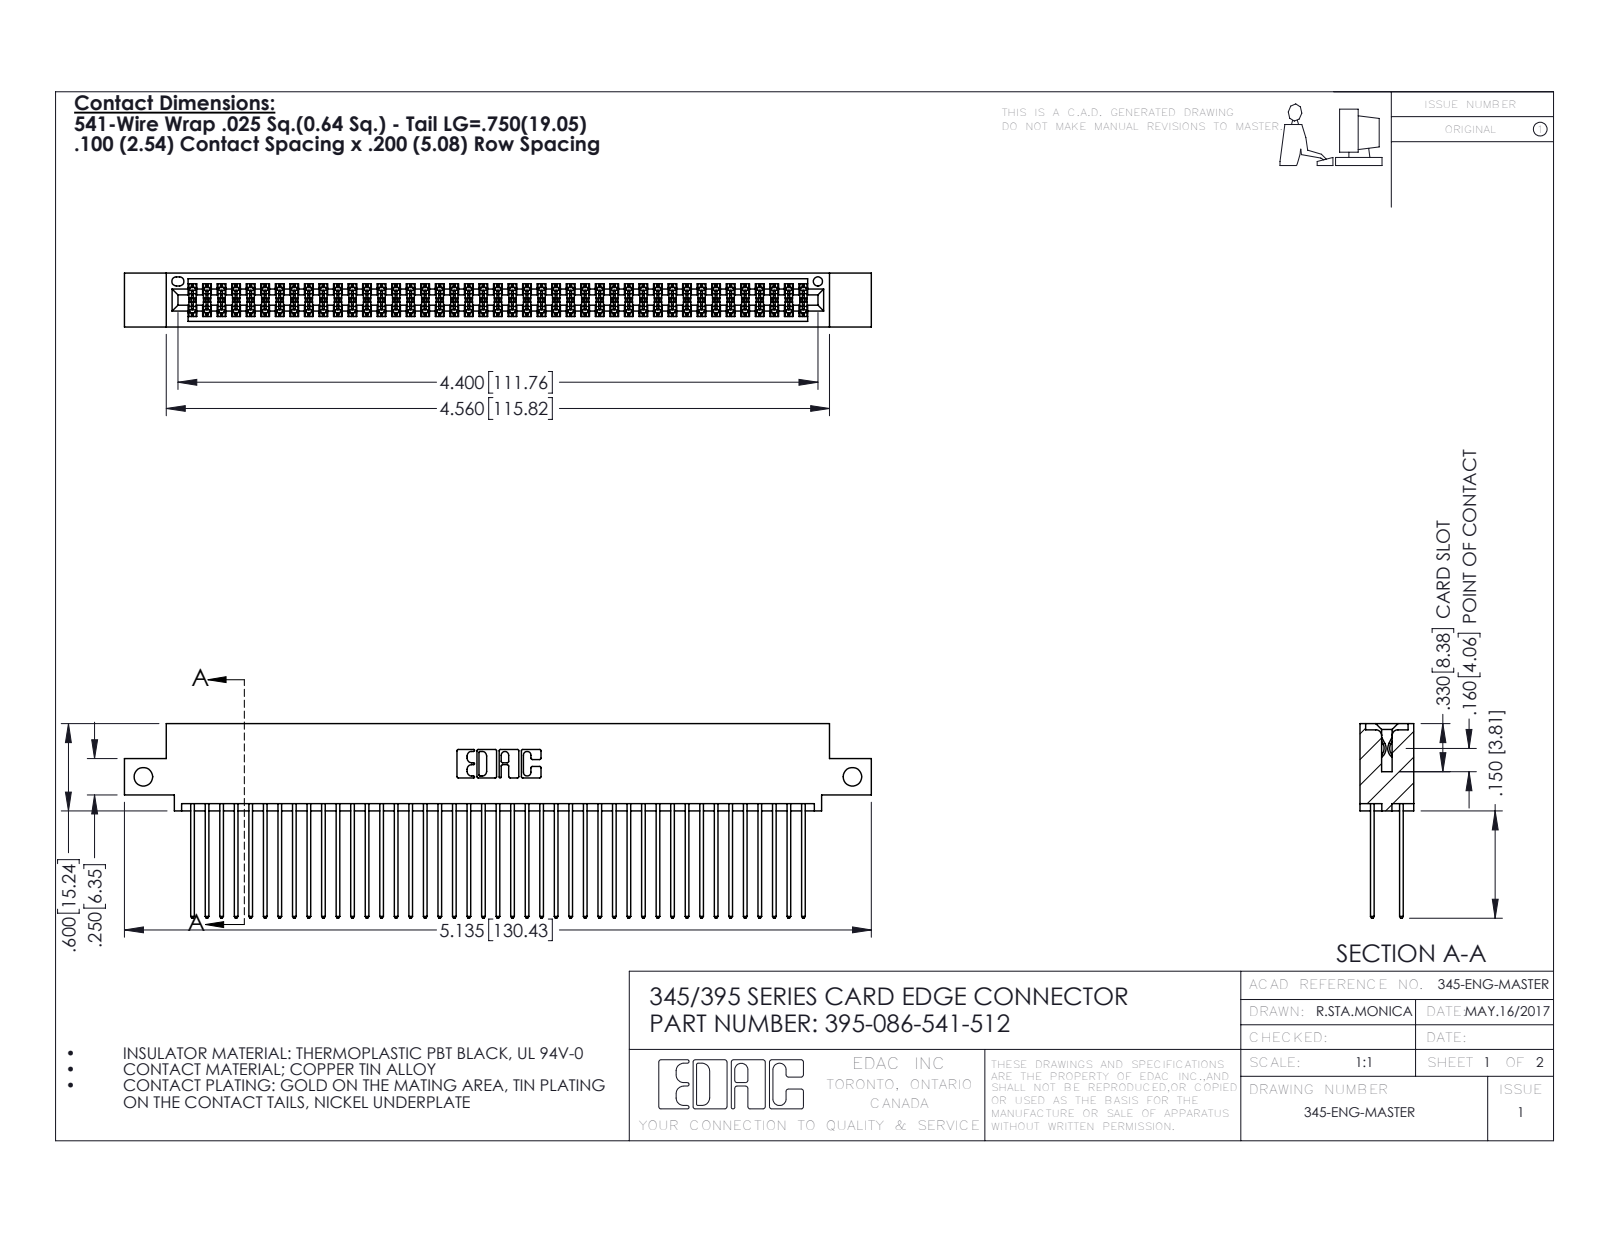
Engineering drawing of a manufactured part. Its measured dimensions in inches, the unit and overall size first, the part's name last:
Units: inches
Overall size (bounding box): 5.135 × 1.337 × 0.37
Round holes (diameter × count): ⌀0.128 ×2, ⌀0.064 ×1
Partial cylindrical surfaces — rounded edges, fillets, slot ends (radius × count): R0.006 ×129, R0.01 ×86, R0.01 ×22, R0.007 ×6, R0.031 ×6, R0.026 ×3, R0.014 ×2, R0.019 ×2
Main face-to-face distances: 0.298, 0.072, 0.2, 0.098, 0.272, 0.025, 0.225, 0.37, 0.175, 0.149
Hole centre spacings: 4.875
Volume: 0.794 in³ · Surface area: 33.37 in²
Bodies: 87 solids, 4430 faces (2922 planar, 1508 cylindrical, 0 other)
Part name (STEP PRODUCT): 345-292-001_345-293-141; 395-086-541-512; 345 Part_0.110 Offset - Side Mount
STEP written by: SolidWorks 2016 (CONFIG_CONTROL_DESIGN)
